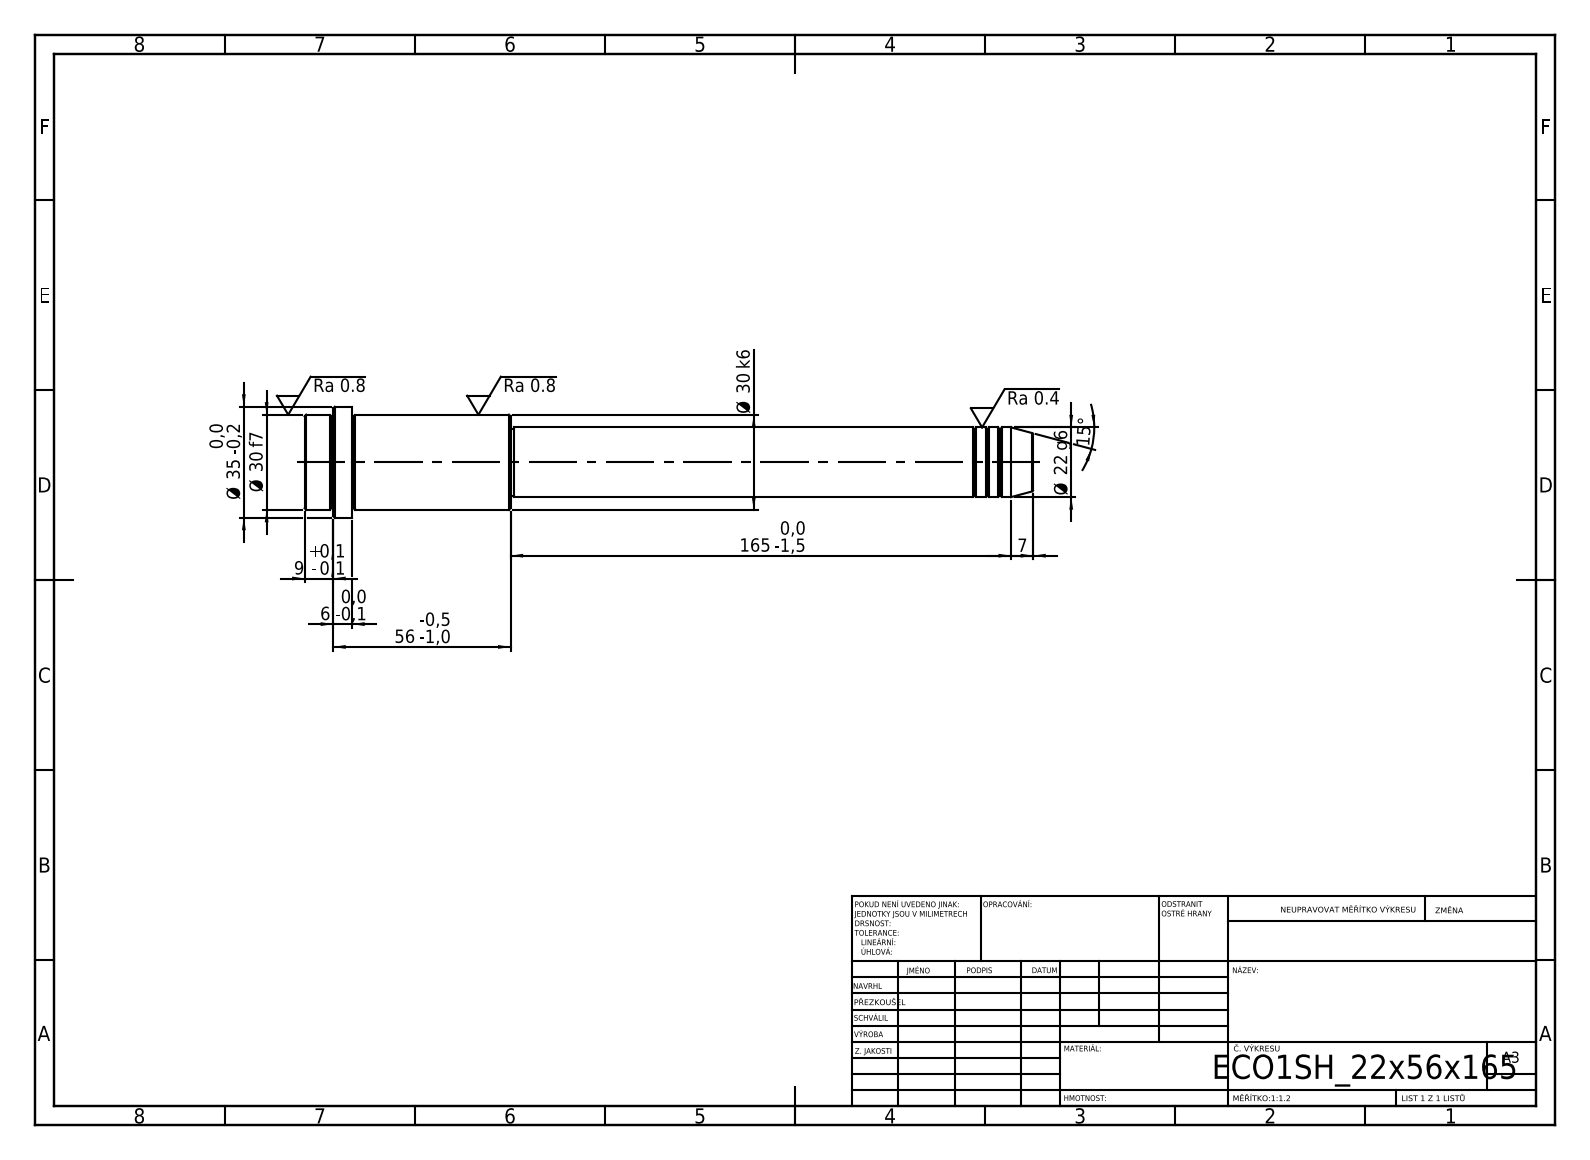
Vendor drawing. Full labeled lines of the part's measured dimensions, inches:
STEP written by: SolidWorks 2019 (CONFIG_CONTROL_DESIGN)
Units: inches
Bodies: 1 solid, 52 faces (6 planar, 16 cylindrical, 30 other)
Overall size (bounding box): 9.055 × 1.378 × 1.378
Volume: 6.685 in³ · Surface area: 30.36 in²
Round bosses / shafts (diameter × count): ⌀1.378 ×1, ⌀1.181 ×1, ⌀0.866 ×1, ⌀0.827 ×1
Main face-to-face distances: 2.559, 1.969, 0.591, 6.496, 8.465, 9.055, 8.701, 2.205, 0.236, 0.354
